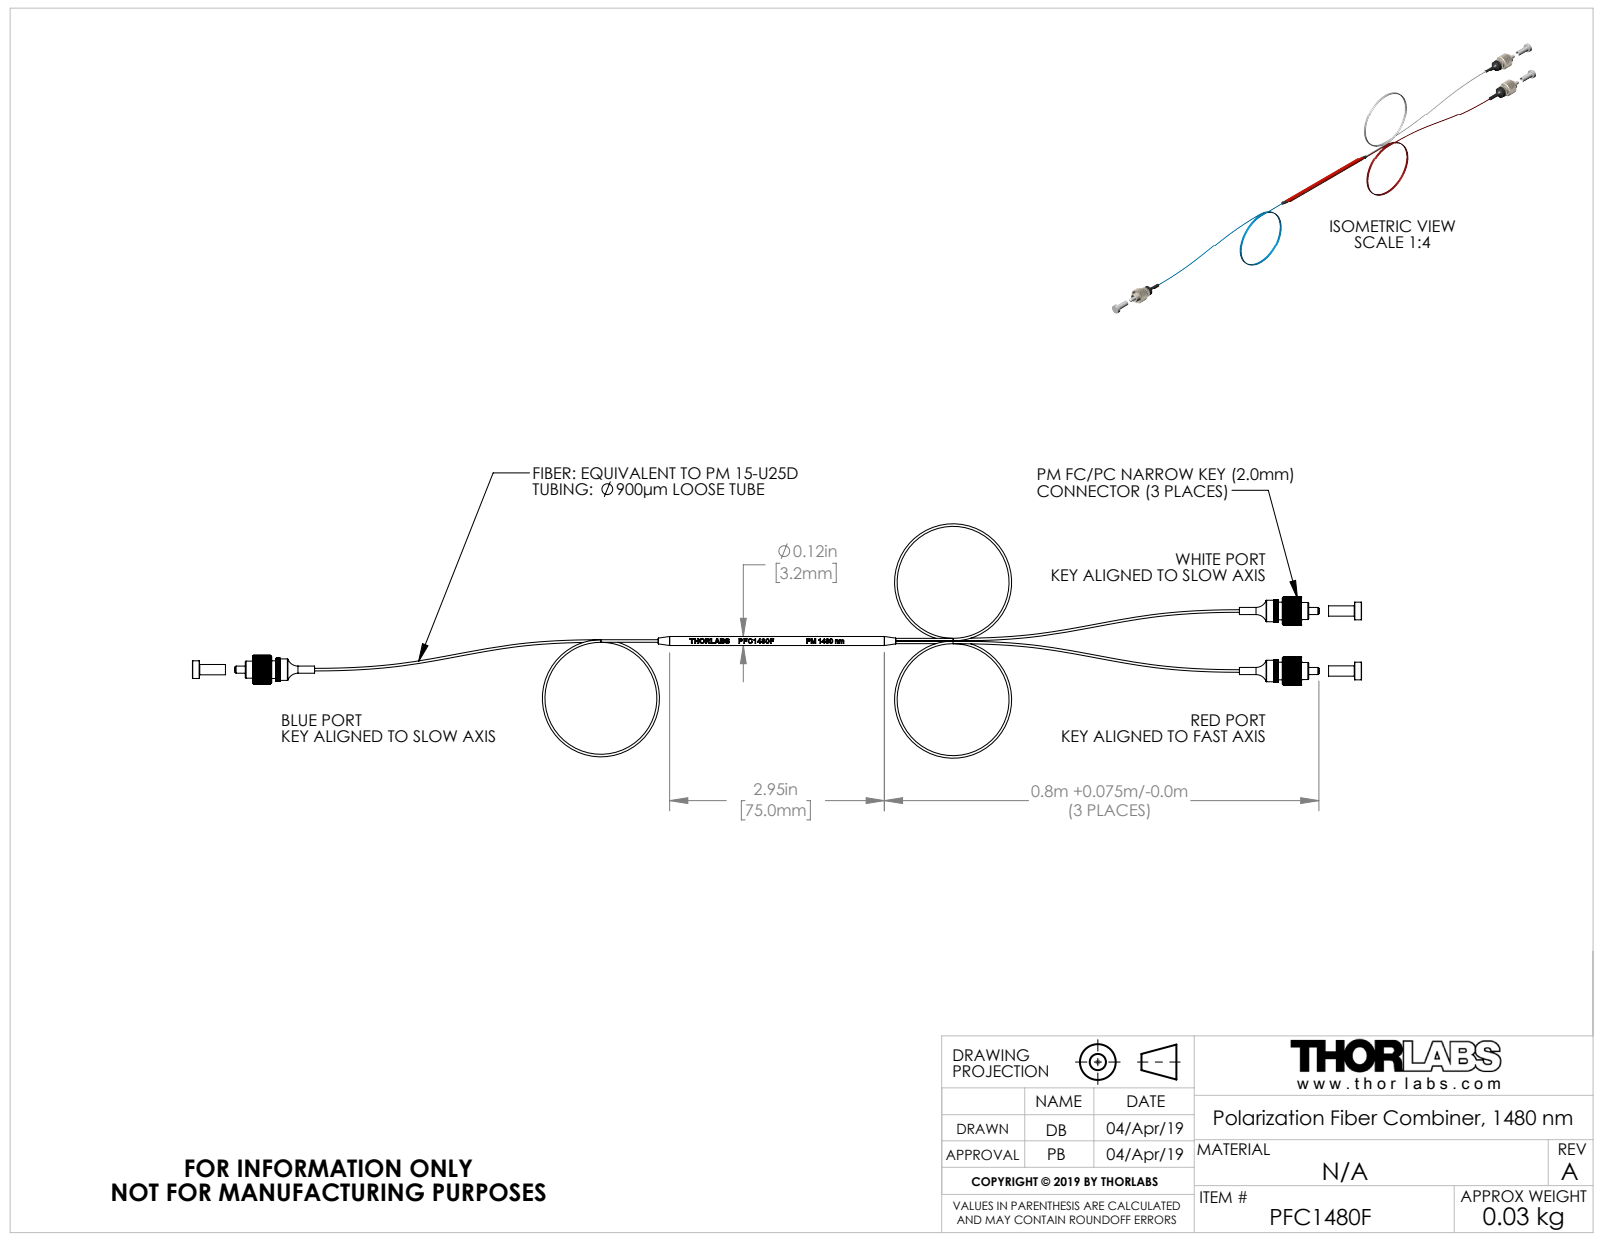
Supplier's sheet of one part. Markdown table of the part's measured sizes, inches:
| quantity | value |
| --- | --- |
| part name | DWG1751_45-2mm; PANDA 1550_60; DWG1631_75mm; DWG1528 (+8 more) |
| STEP written by | SolidWorks 2018 (CONFIG_CONTROL_DESIGN) |
| units | inches |
| bodies | 32 solids, 2611 faces (1271 planar, 890 cylindrical, 450 other) |
| overall size | 16.075 × 3.222 × 0.551 |
| volume | 0.2 in³ |
| surface area | 21.06 in² |
| round holes (diameter × count) | 0.02 × 6, 0.035 × 3, 0.037 × 3, 0.039 × 3, 0.098 × 3, 0.11 × 3, 0.132 × 3, 0.172 × 3, 0.173 × 3, 0.2 × 3, 0.219 × 3, 0.24 × 3 |
| round bosses / shafts (diameter × count) | 0.295 × 3, 0.278 × 3, 0.243 × 3, 0.239 × 3, 0.234 × 3, 0.212 × 3, 0.191 × 3, 0.142 × 3 |
| partial cylindrical surfaces (radius × count) | 0.02 × 6, 0.03 × 3, 0.061 × 3, 0.089 × 3, 0.157 × 3, 0.197 × 3, 0.018 × 2, 0.039 × 1 |
| main face-to-face distances | 0.27, 0.27, 0.079, 0.056, 0.196, 0.117, 13.778, 0.061, 0.135, 1.09 |
| hole center spacings | 0.402, 0.42, 0.438, 0.019, 0.019, 0.037, 0.159, 0.383 |
